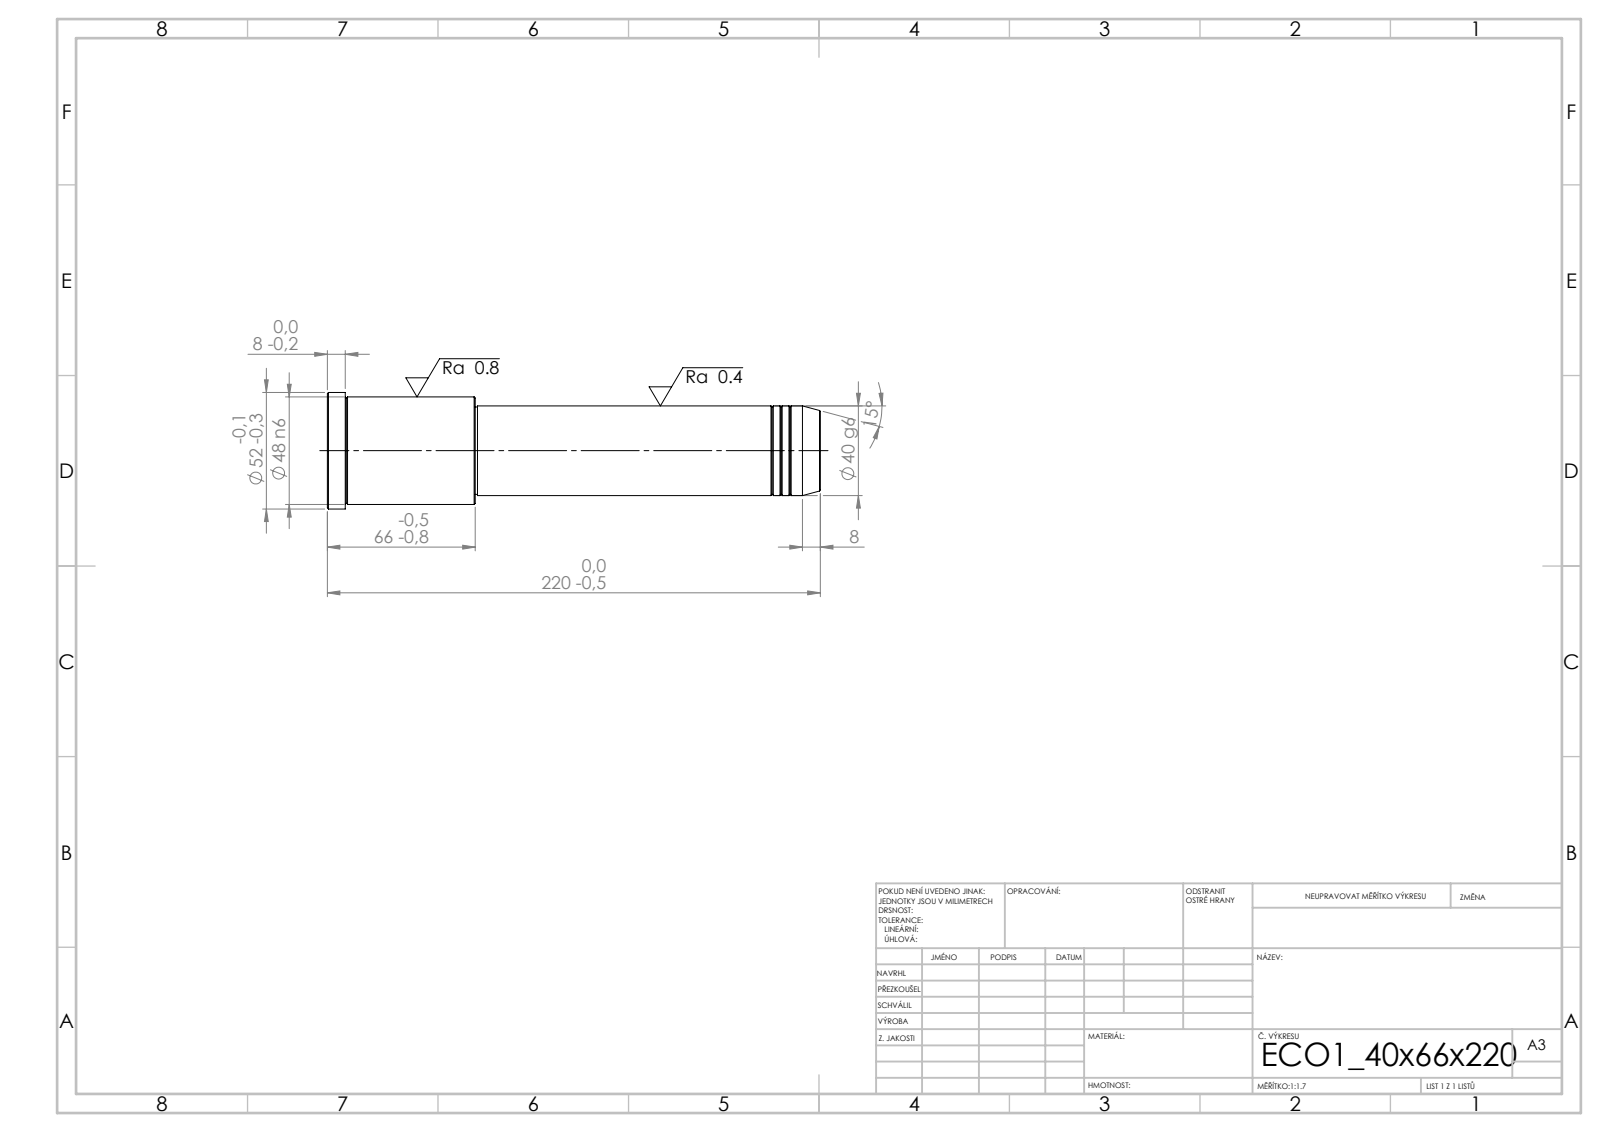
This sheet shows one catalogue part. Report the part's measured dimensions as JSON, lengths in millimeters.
{"step_written_by": "SolidWorks 2019 (CONFIG_CONTROL_DESIGN)", "units": "millimeters", "bodies": {"solids": 1, "faces": 43, "planar": 5, "cylindrical": 14, "other": 24}, "overall_size": [220, 52, 52], "volume_mm3": 314118, "surface_area_mm2": 33682, "round_bosses_or_shafts": [[52, 1], [48, 1], [40, 1], [39, 1]], "face_to_face_distances": [220, 154, 66, 212, 58, 8, 153, 1, 59, 67]}
